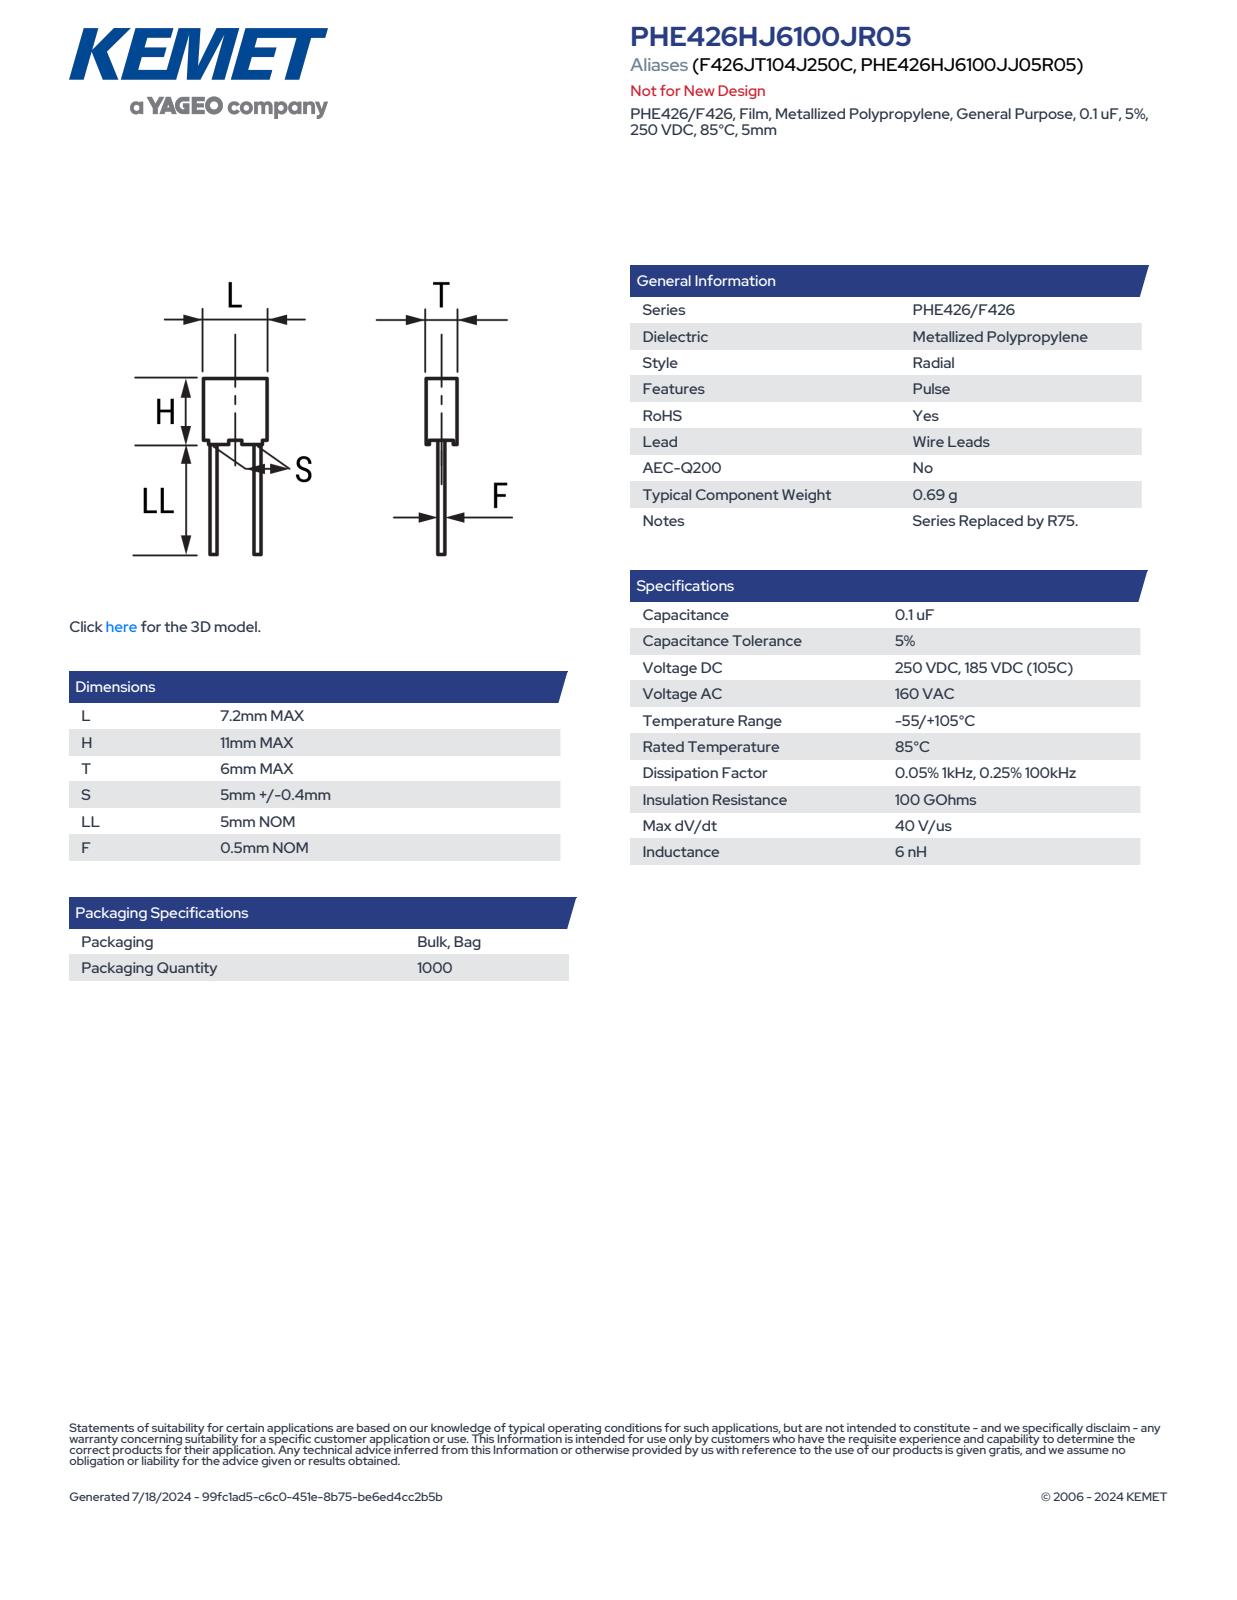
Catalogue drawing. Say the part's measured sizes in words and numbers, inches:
The part is named "CFR_RB3_7.2X11X6_L7.2H11T6S5LL5F0.5". Its 3-D file was written by "SolidWorks 2014 (AUTOMOTIVE_DESIGN)". It is 4 solids with 85 faces: 77 planar, 8 cylindrical and 0 other. Overall it measures 0.63 by 0.283 by 0.236 inches. Its volume is 0.027 cubic inches and its surface area 0.634 square inches. Round bosses or shafts: 2 of diameter 0.02. Partial cylindrical surfaces (rounded edges, fillets, slot ends): 4 of radius 0.02. The main face-to-face distances are 0.236, 0.283, 0.404, 0.227, 0.274, 0.03, 0.433, 0.217, 0.265, 0.015.
